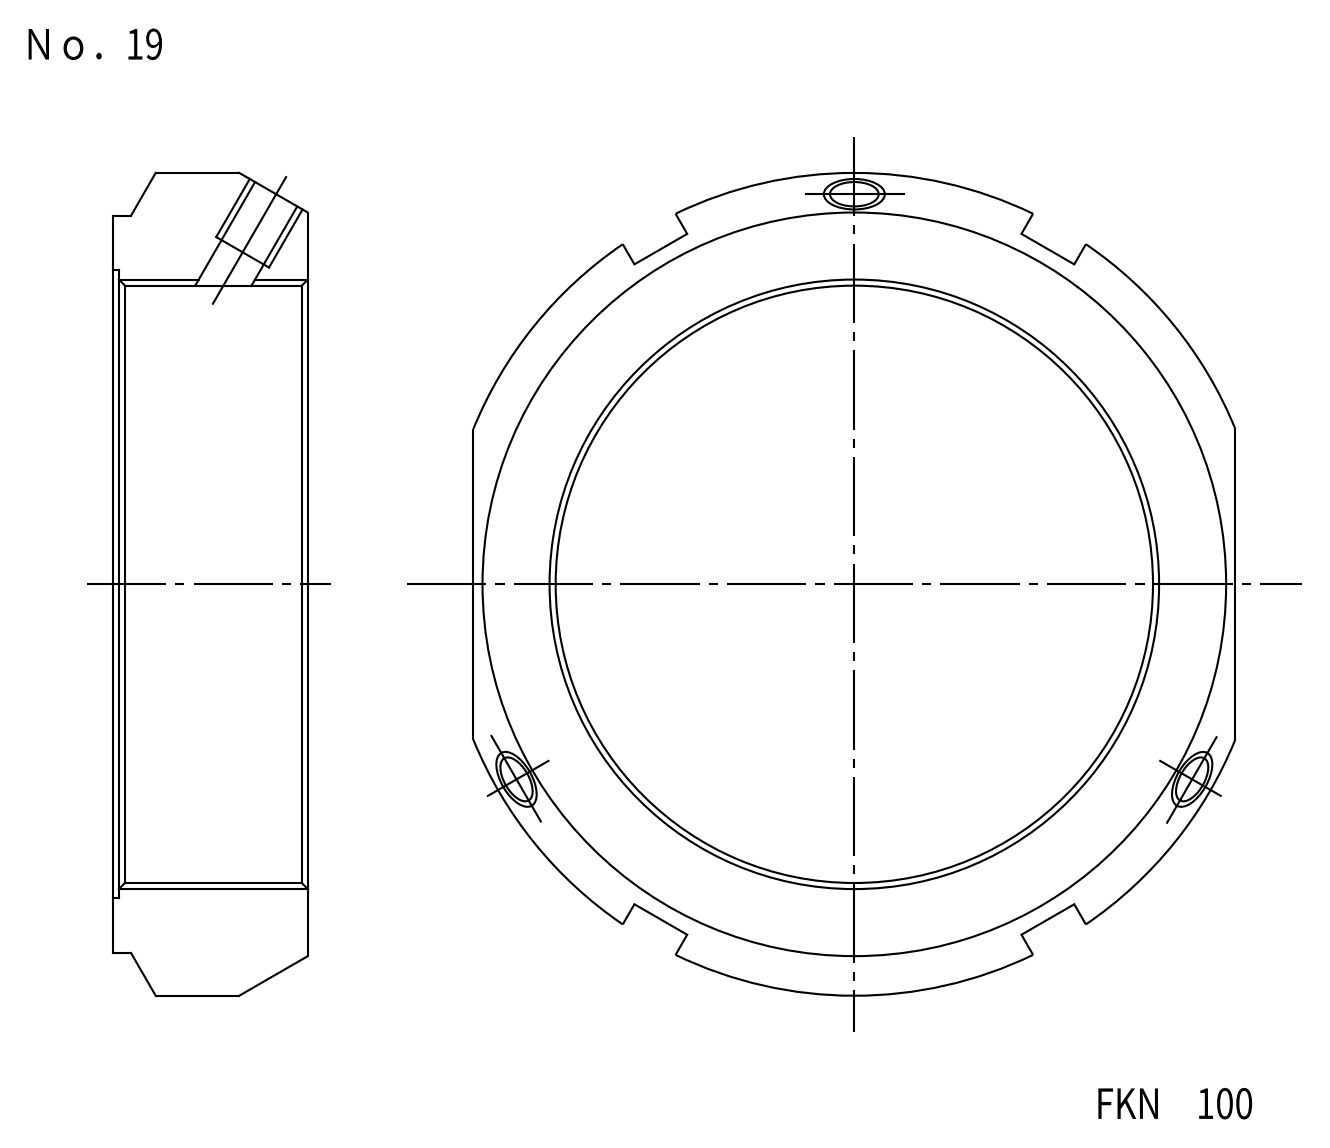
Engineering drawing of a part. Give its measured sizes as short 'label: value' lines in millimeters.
name: FKD FKN100
written by: Autodesk Inventor LT (CONFIG_CONTROL_DESIGN)
unit: mm
bodies: 1 solid, 37 faces (20 planar, 15 cylindrical, 2 other)
size: 135 × 125 × 32
volume: 164 951 mm³; area: 33 988 mm²
holes: 3× ⌀8.38, 3× ⌀10.2, 1× ⌀100, 1× ⌀103
bosses: 1× ⌀121
rounds: 1× R67.5
face distances: 32, 125, 1.5, 30.5, 127, 10
